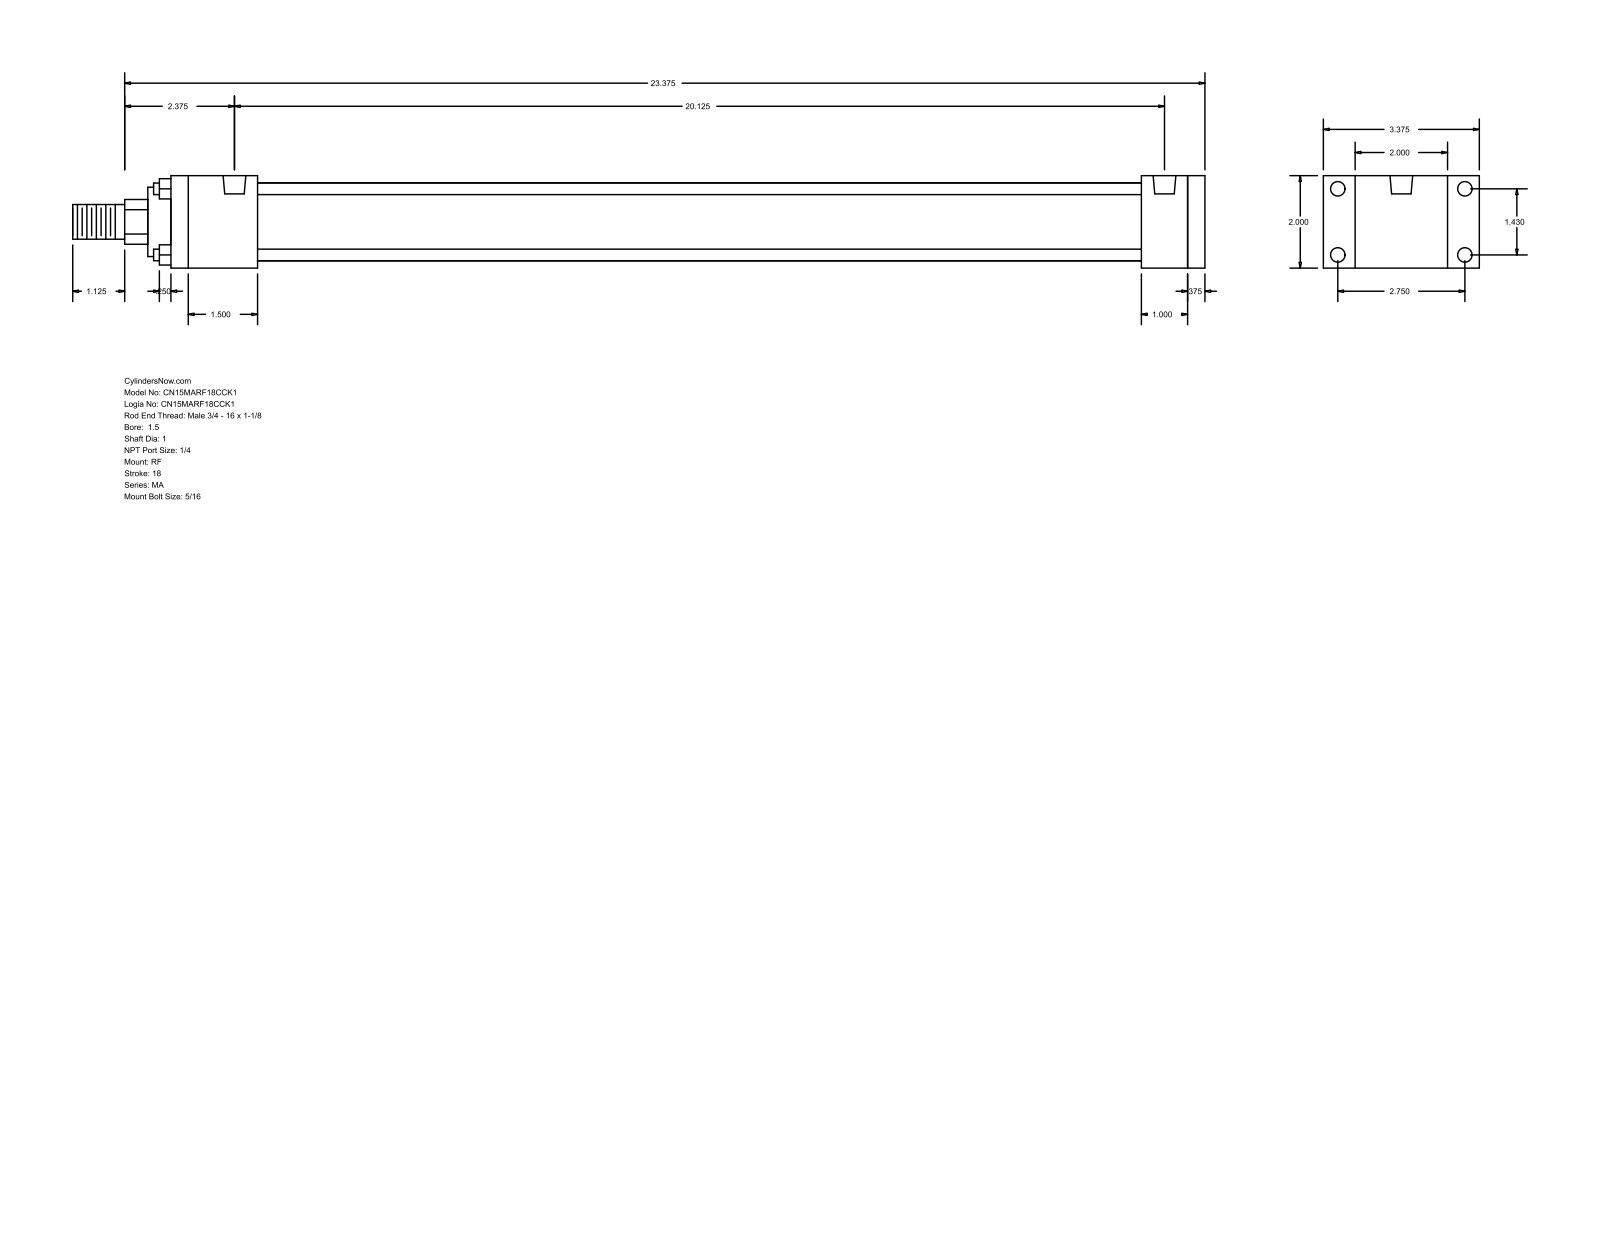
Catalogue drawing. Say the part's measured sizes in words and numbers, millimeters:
The part is named "MA_RF__0150_1". Its 3-D file was written by "GSSL Pune (CONFIG_CONTROL_DESIGN)". It is 0 solids with 92 faces: 64 planar, 28 cylindrical and 0 other. Overall it measures 622.3 by 85.72 by 50.8 millimeters. Round holes: 8 of diameter 7.94, 2 of diameter 12.49. Round bosses or shafts: 4 of diameter 6.35, 1 of diameter 42.93, 1 of diameter 38.1, 1 of diameter 25.4, 1 of diameter 19.05. Partial cylindrical surfaces (rounded edges, fillets, slot ends): 1 of radius 12.29. The main face-to-face distances are 50.8, 9.53, 558.8, 25.4, 568.33, 533.4, 34.93, 47.63, 485.77, 511.17. The hole center spacings are 36.32, 69.84, 78.72, 511.17.
